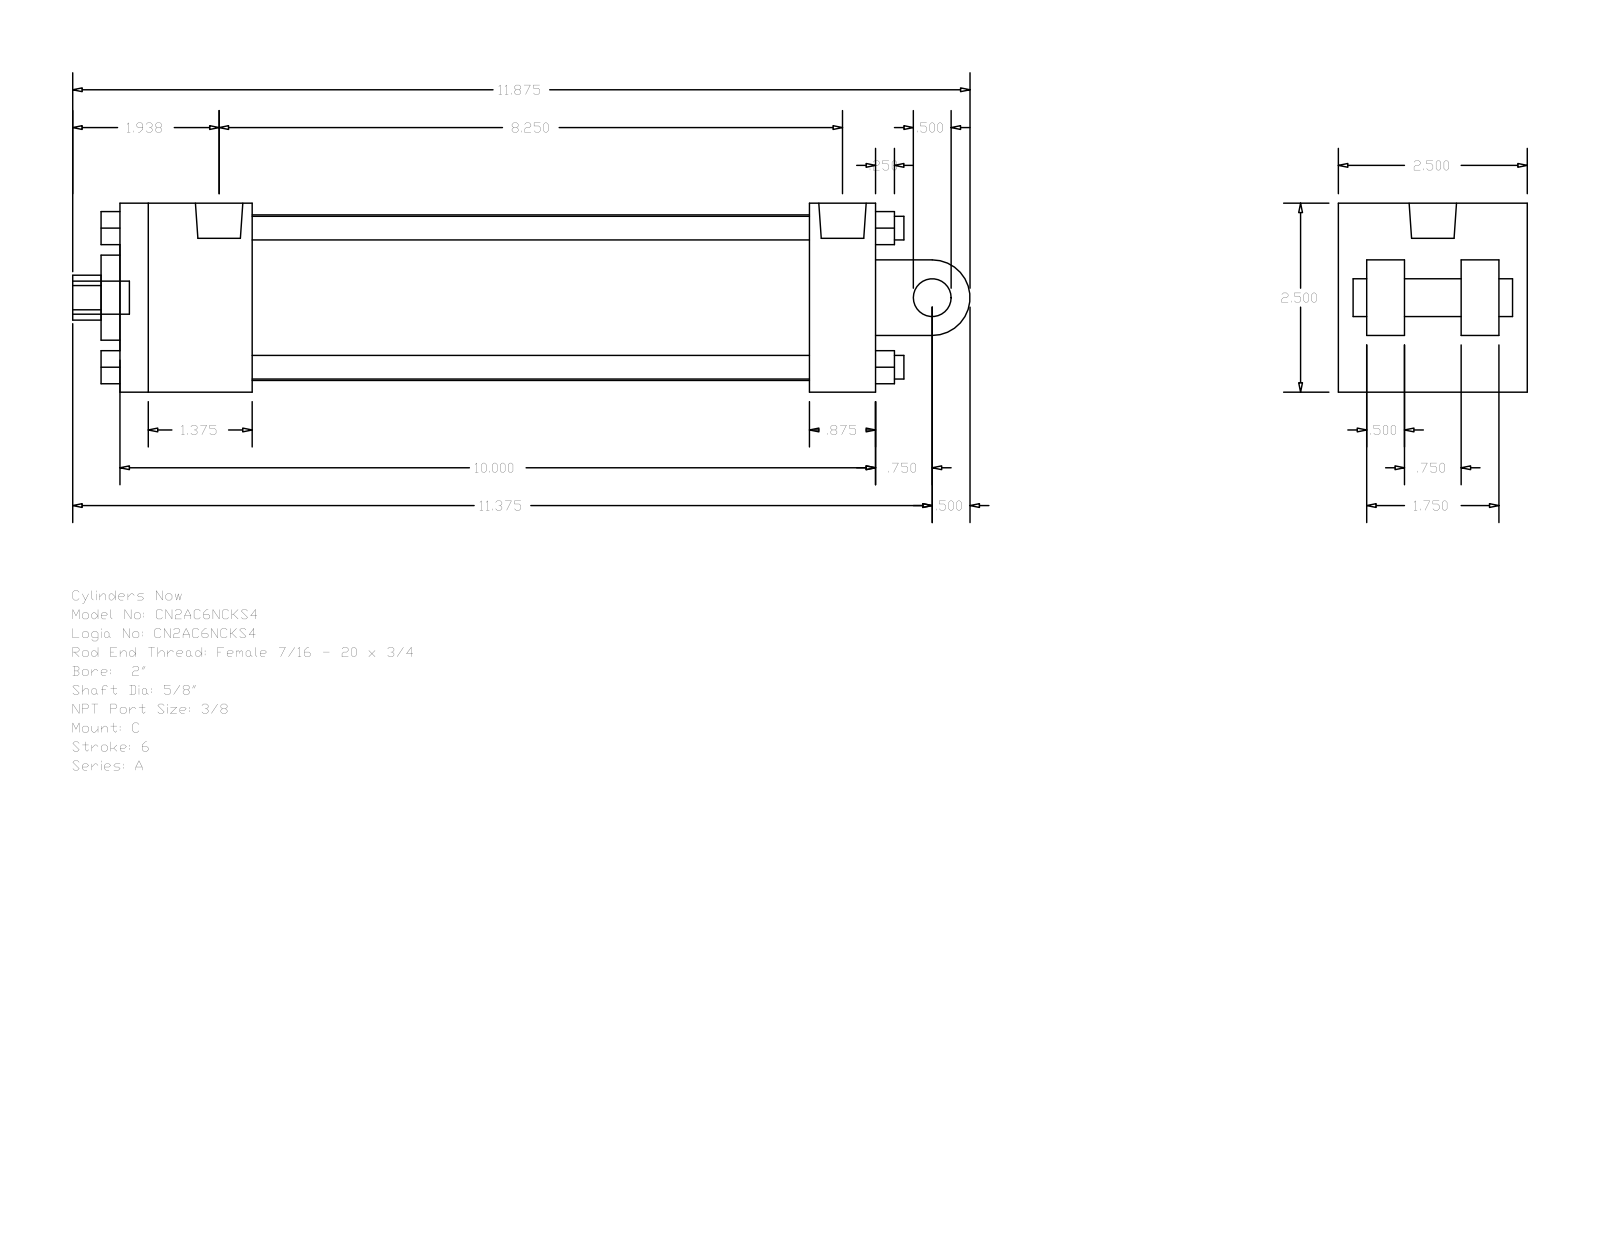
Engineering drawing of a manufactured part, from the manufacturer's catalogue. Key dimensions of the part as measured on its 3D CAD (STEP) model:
Part name (STEP PRODUCT): A_C__0200_0.625
STEP written by: GSSL Pune (CONFIG_CONTROL_DESIGN)
Units: millimetres
Bodies: 0 solids, 135 faces (102 planar, 33 cylindrical, 0 other)
Overall size (bounding box): 301.62 × 63.5 × 63.5
Round holes (diameter × count): ⌀5.56 ×2, ⌀15.88 ×1, ⌀15.93 ×1, ⌀28.57 ×1, ⌀55.63 ×1
Round bosses / shafts (diameter × count): ⌀7.94 ×4, ⌀5.56 ×2, ⌀15.93 ×1, ⌀12.7 ×1, ⌀11.11 ×1
Partial cylindrical surfaces — rounded edges, fillets, slot ends (radius × count): R7.54 ×1, R12.7 ×1
Main face-to-face distances: 63.5, 254, 44.45, 9.52, 209.55, 231.77, 187.32, 22.23, 12.7, 41.28
Hole centre spacings: 3.97
